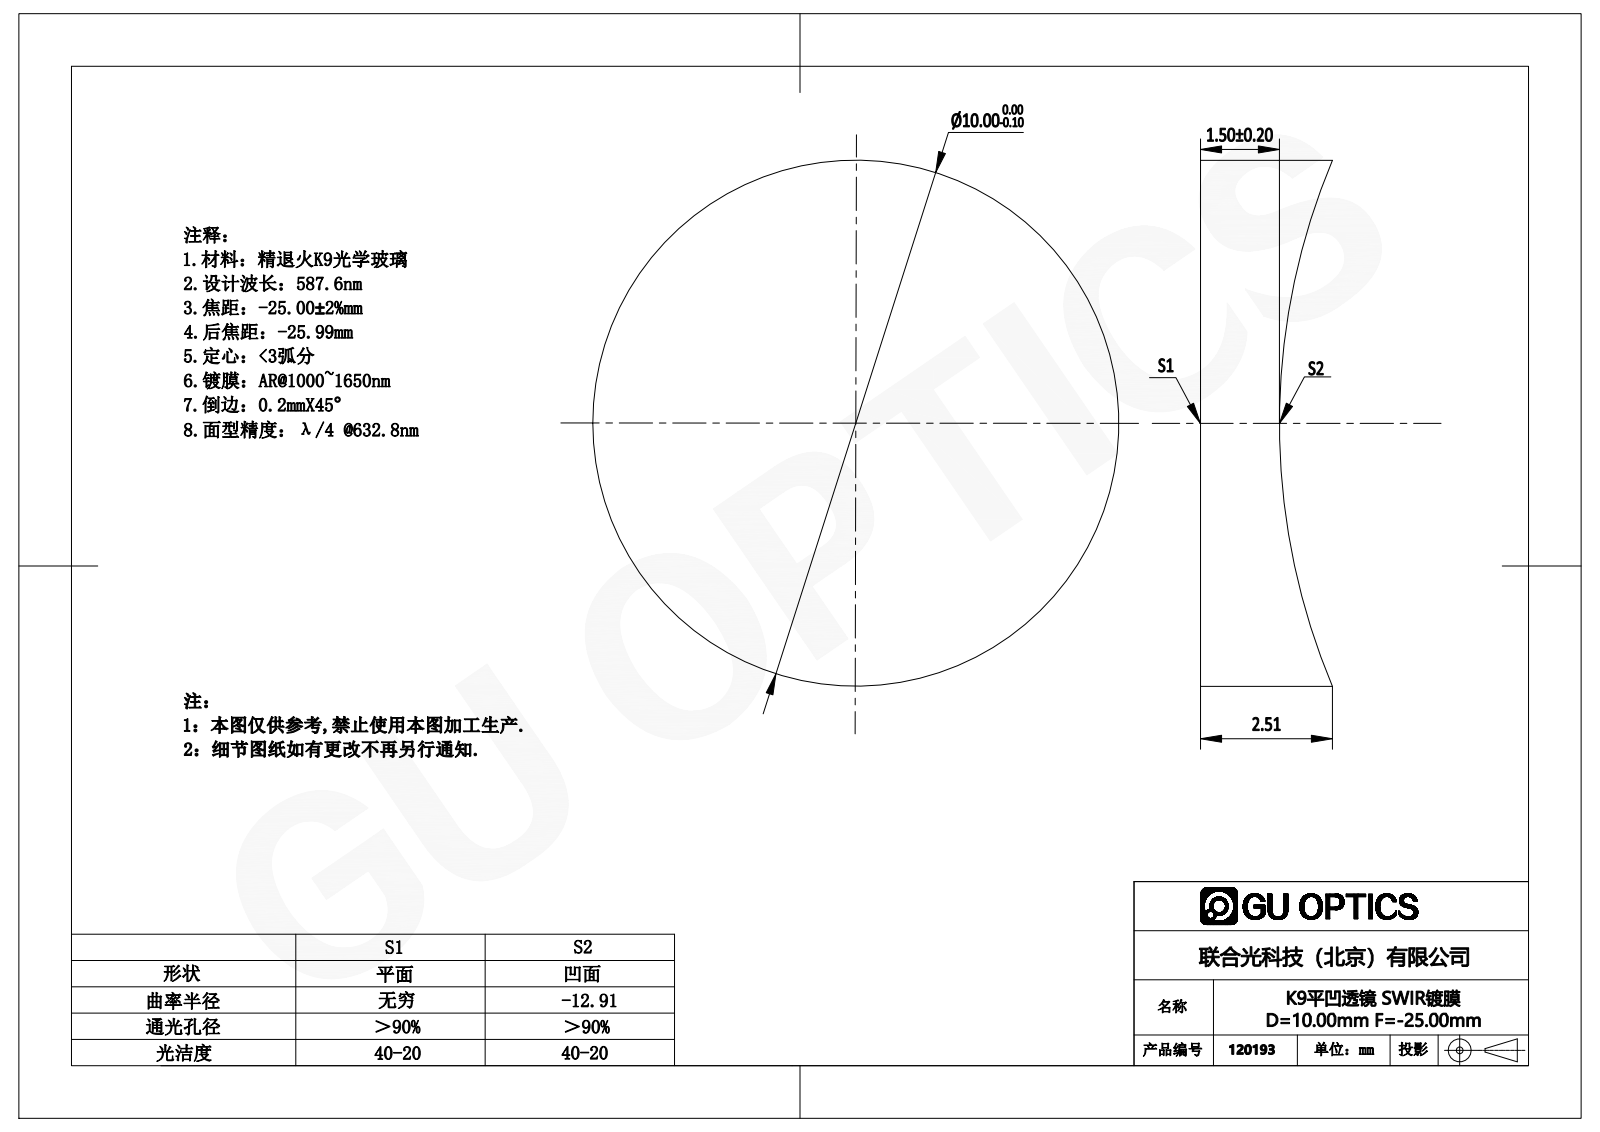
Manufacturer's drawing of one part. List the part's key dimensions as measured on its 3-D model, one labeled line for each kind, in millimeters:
Part name (STEP PRODUCT): 120133
STEP written by: SolidWorks 2016 (AUTOMOTIVE_DESIGN)
Units: millimetres
Bodies: 1 solid, 5 faces (1 planar, 2 cylindrical, 2 other)
Overall size (bounding box): 10 × 10 × 2.51
Volume: 157 mm³ · Surface area: 239 mm²
Round bosses / shafts (diameter × count): ⌀10 ×1
